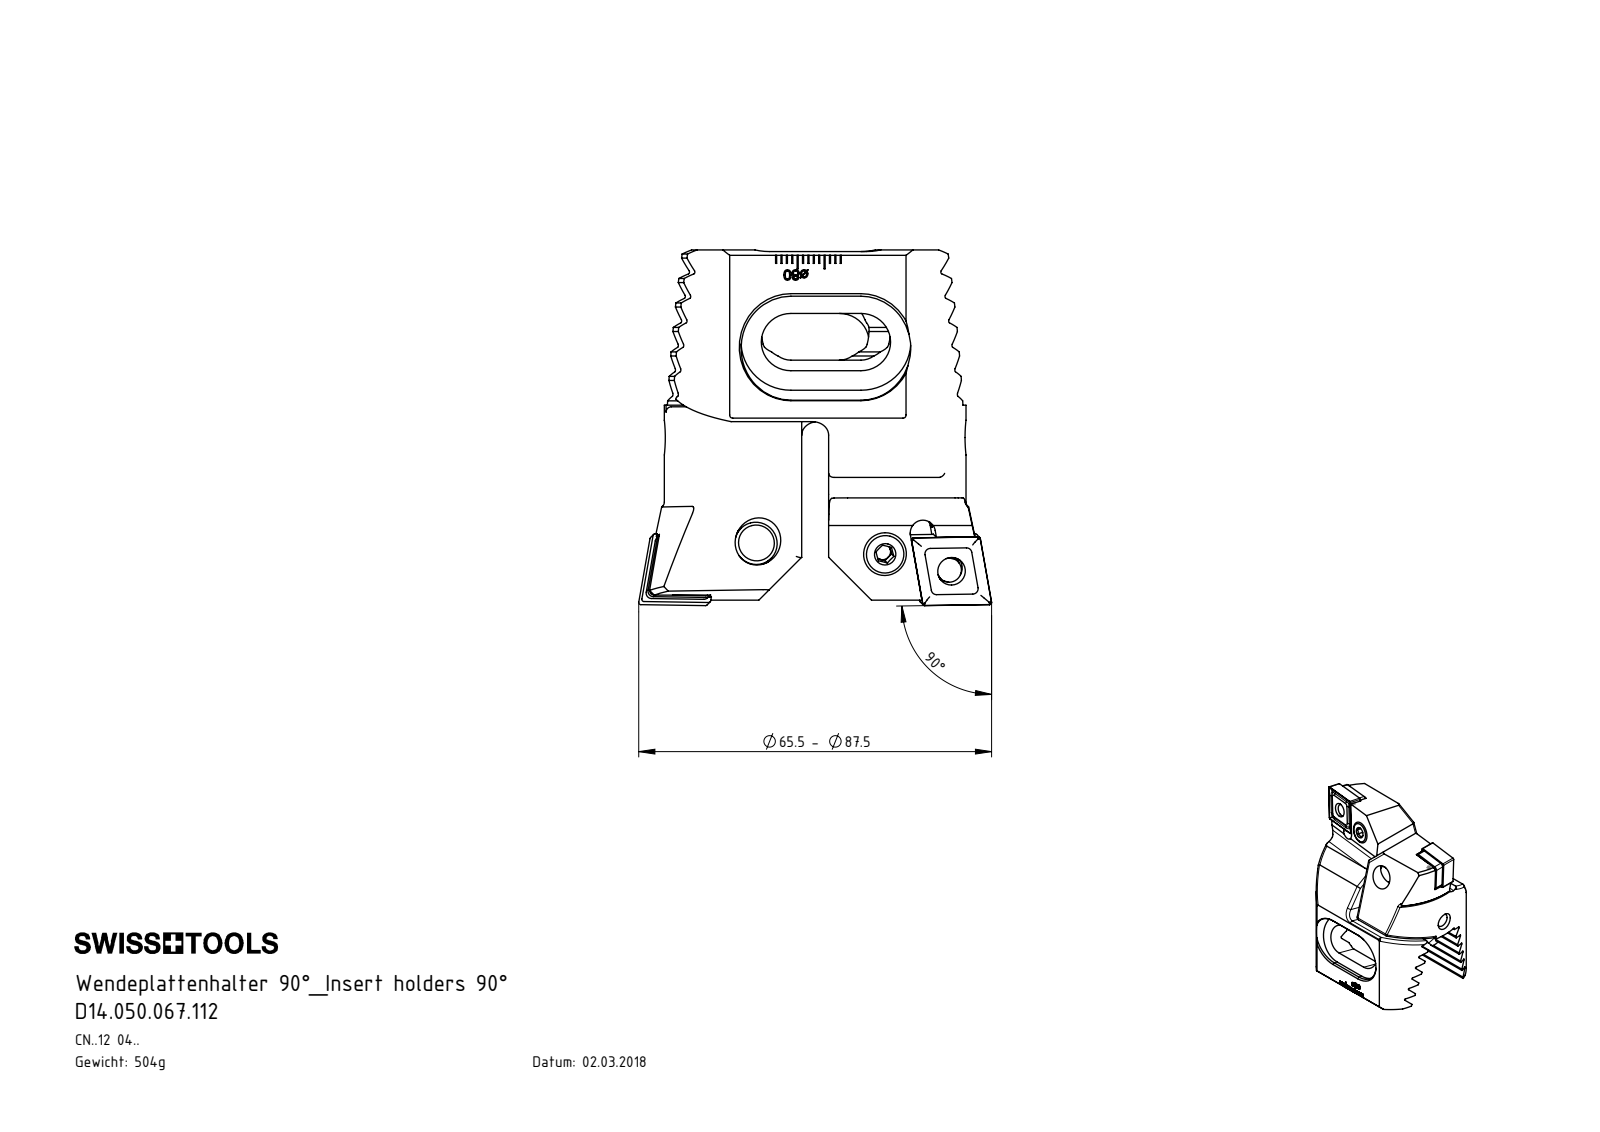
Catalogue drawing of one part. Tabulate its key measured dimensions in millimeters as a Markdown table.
| quantity | value |
| --- | --- |
| part name | Z55-xxx.001.037_C_CN12; WCD-ER4.101.017_A; WCD-ER3.101.000_A; WCD (+5 more) |
| STEP written by | SolidWorks 2017 (CONFIG_CONTROL_DESIGN) |
| units | millimeters |
| bodies | 14 solids, 876 faces (424 planar, 170 cylindrical, 282 other) |
| overall size | 65.98 × 65.5 × 44.2 |
| volume | 63 396 mm³ |
| surface area | 26 305 mm² |
| round holes (diameter × count) | 2 × 2, 5.16 × 2, 6.4 × 2, 7 × 2, 8.4 × 2, 5 × 1 |
| round bosses / shafts (diameter × count) | 8 × 2, 7.9 × 2, 6.4 × 2, 4.5 × 2, 3.55 × 2, 6 × 1, 4 × 1 |
| partial cylindrical surfaces (radius × count) | 1 × 22, 0.34 × 12, 0.4 × 8, 2.5 × 6, 3 × 6, 5.5 × 4, 9.25 × 4, 12 × 4 |
| main face-to-face distances | 4.07, 8.14, 12.21, 16.28, 20.35, 7.85, 1.69, 5, 0.5, 44.2 |
| hole center spacings | 12.81, 12.86, 16, 30.9 |
